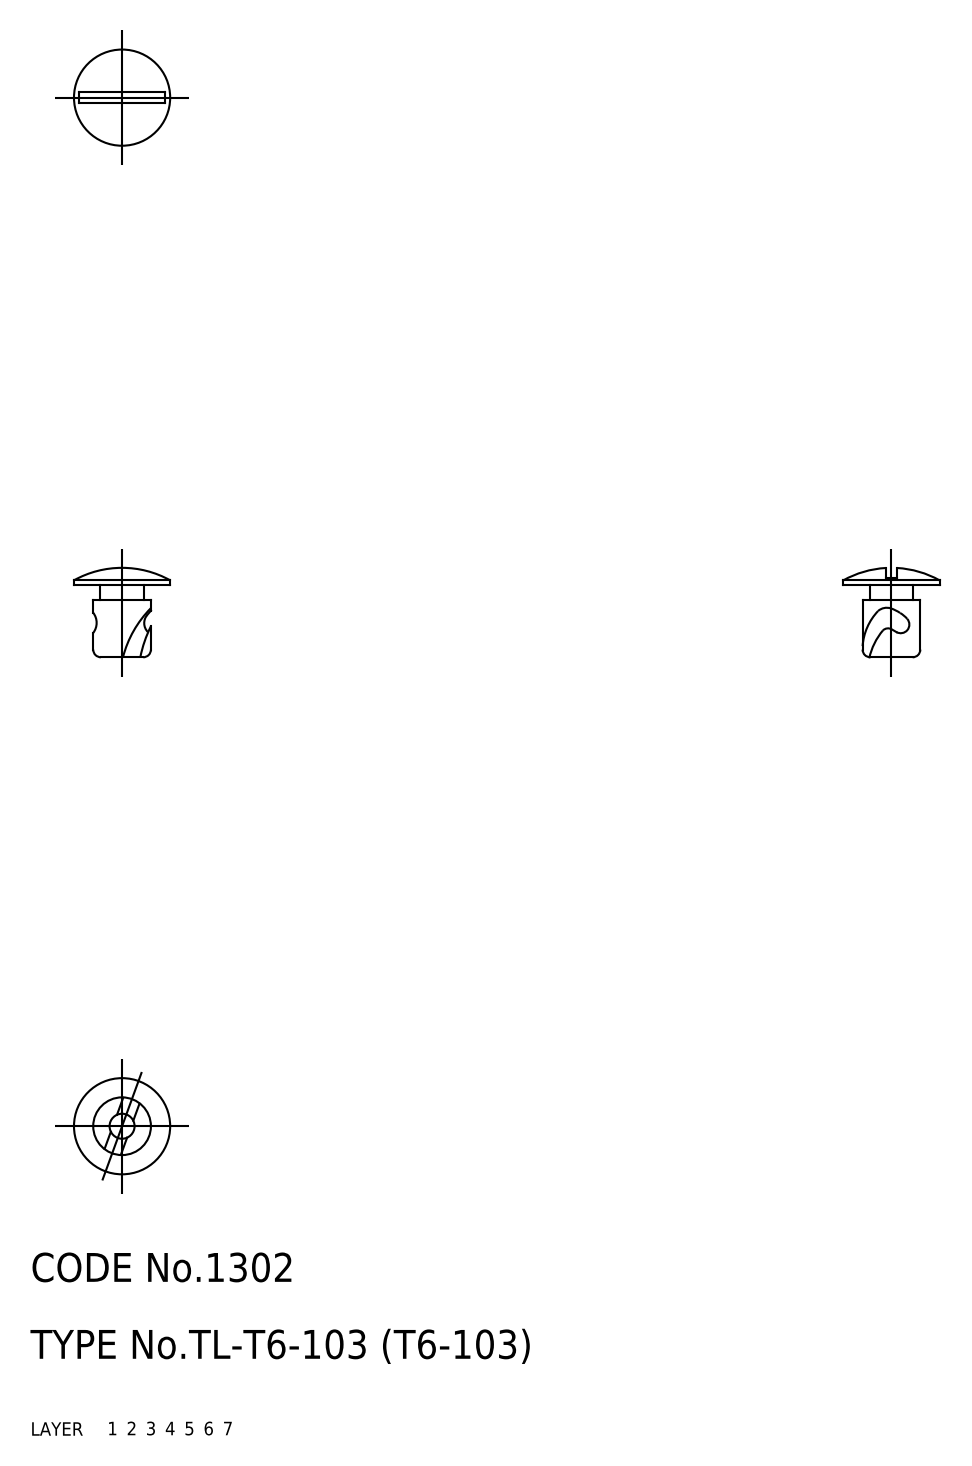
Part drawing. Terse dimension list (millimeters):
name: 67114393
written by: CADfix (AUTOMOTIVE_DESIGN)
unit: mm
bodies: 1 solid, 35 faces (0 planar, 0 cylindrical, 35 other)
size: 10 × 10 × 9.18
volume: 209 mm³; area: 378 mm²
